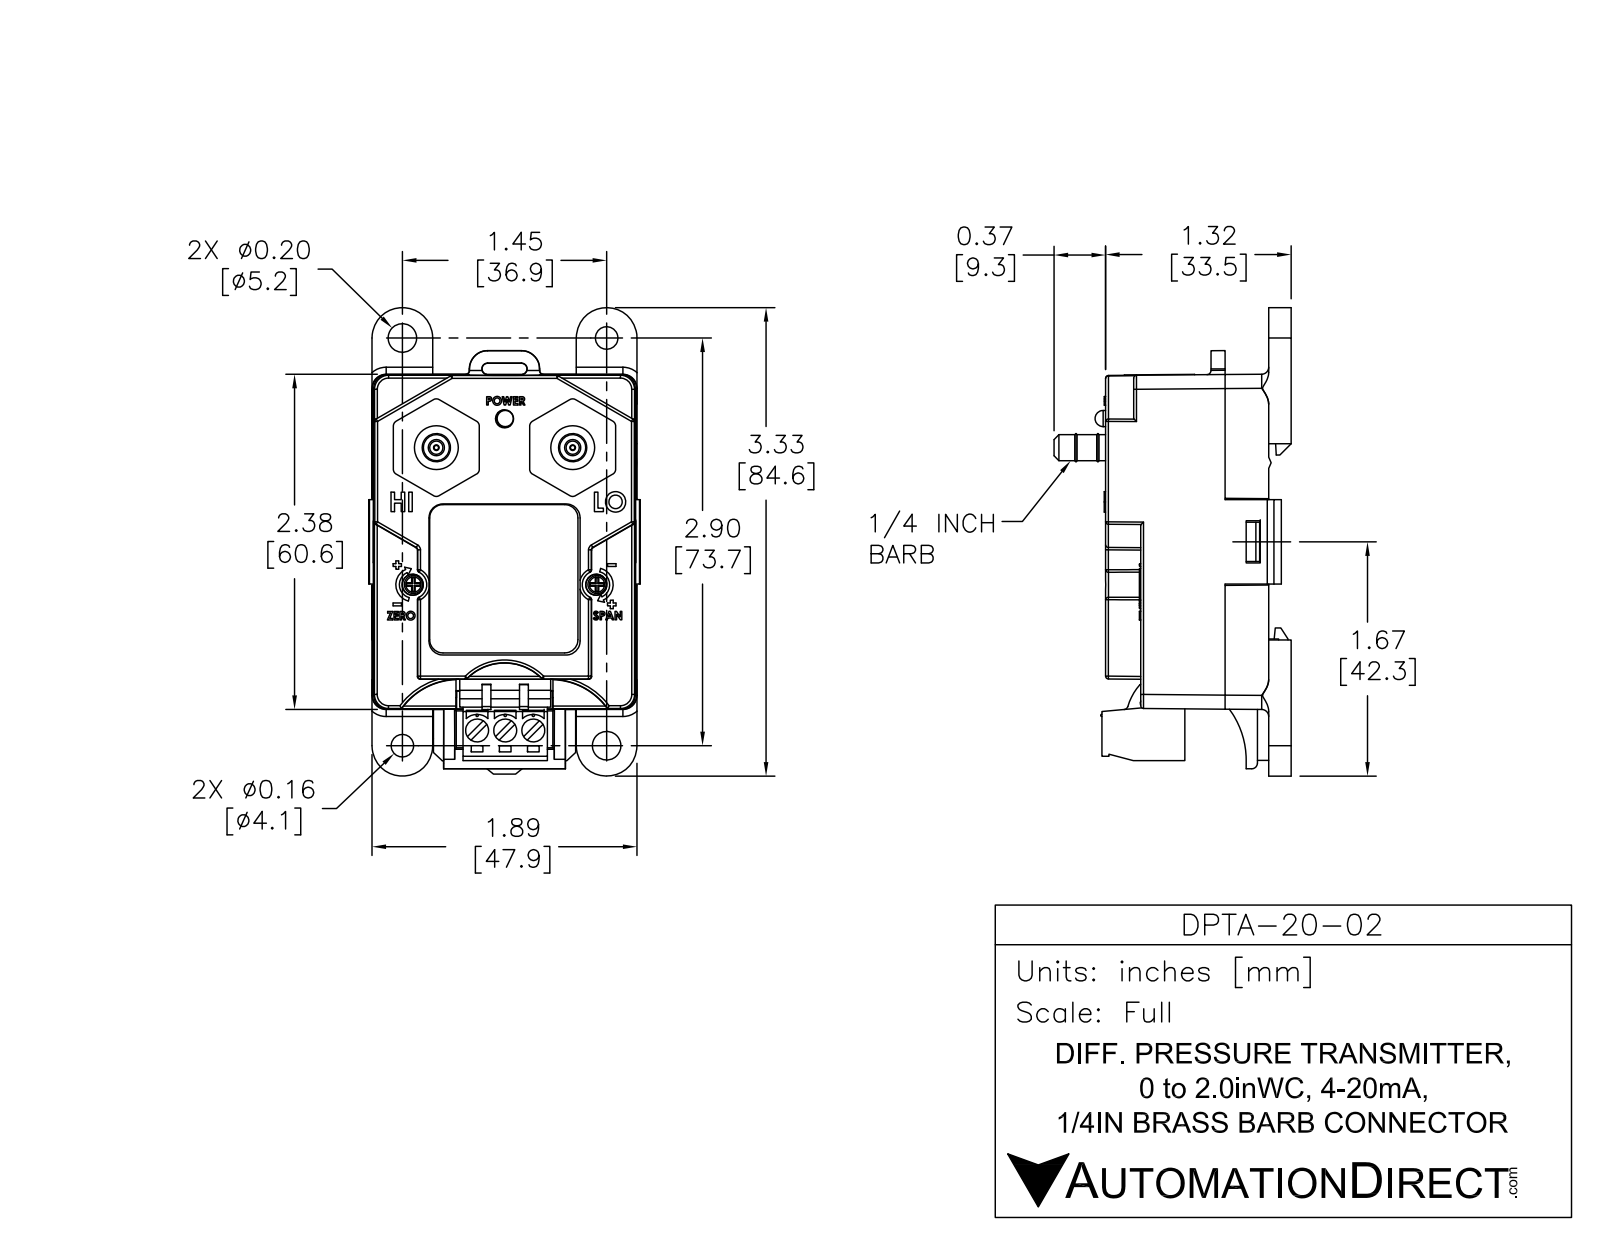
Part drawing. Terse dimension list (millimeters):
name: DPTA-20-02
written by: SolidWorks 2011 (AUTOMOTIVE_DESIGN)
unit: mm
bodies: 11 solids, 448 faces (354 planar, 85 cylindrical, 9 other)
size: 85.01 × 49.76 × 43.1
volume: 29 684 mm³; area: 34 743 mm²
holes: 7× ⌀4, 2× ⌀2.5, 2× ⌀5.12, 1× ⌀3.1
bosses: 3× ⌀5, 3× ⌀3.5, 3× ⌀3.5, 2× ⌀8, 2× ⌀4.75, 1× ⌀3
rounds: 12× R3, 4× R2, 4× R5.5, 2× R0.99, 2× R1.06, 2× R1.12, 2× R2.38, 2× R3.25
face distances: 1, 1.9, 4, 29.1, 0.5, 46.9, 5.9, 5, 33.1, 27.2
hole spacings: 13.55, 20.73, 23.37, 24.92, 29.43, 34.46, 36.67, 38.22
